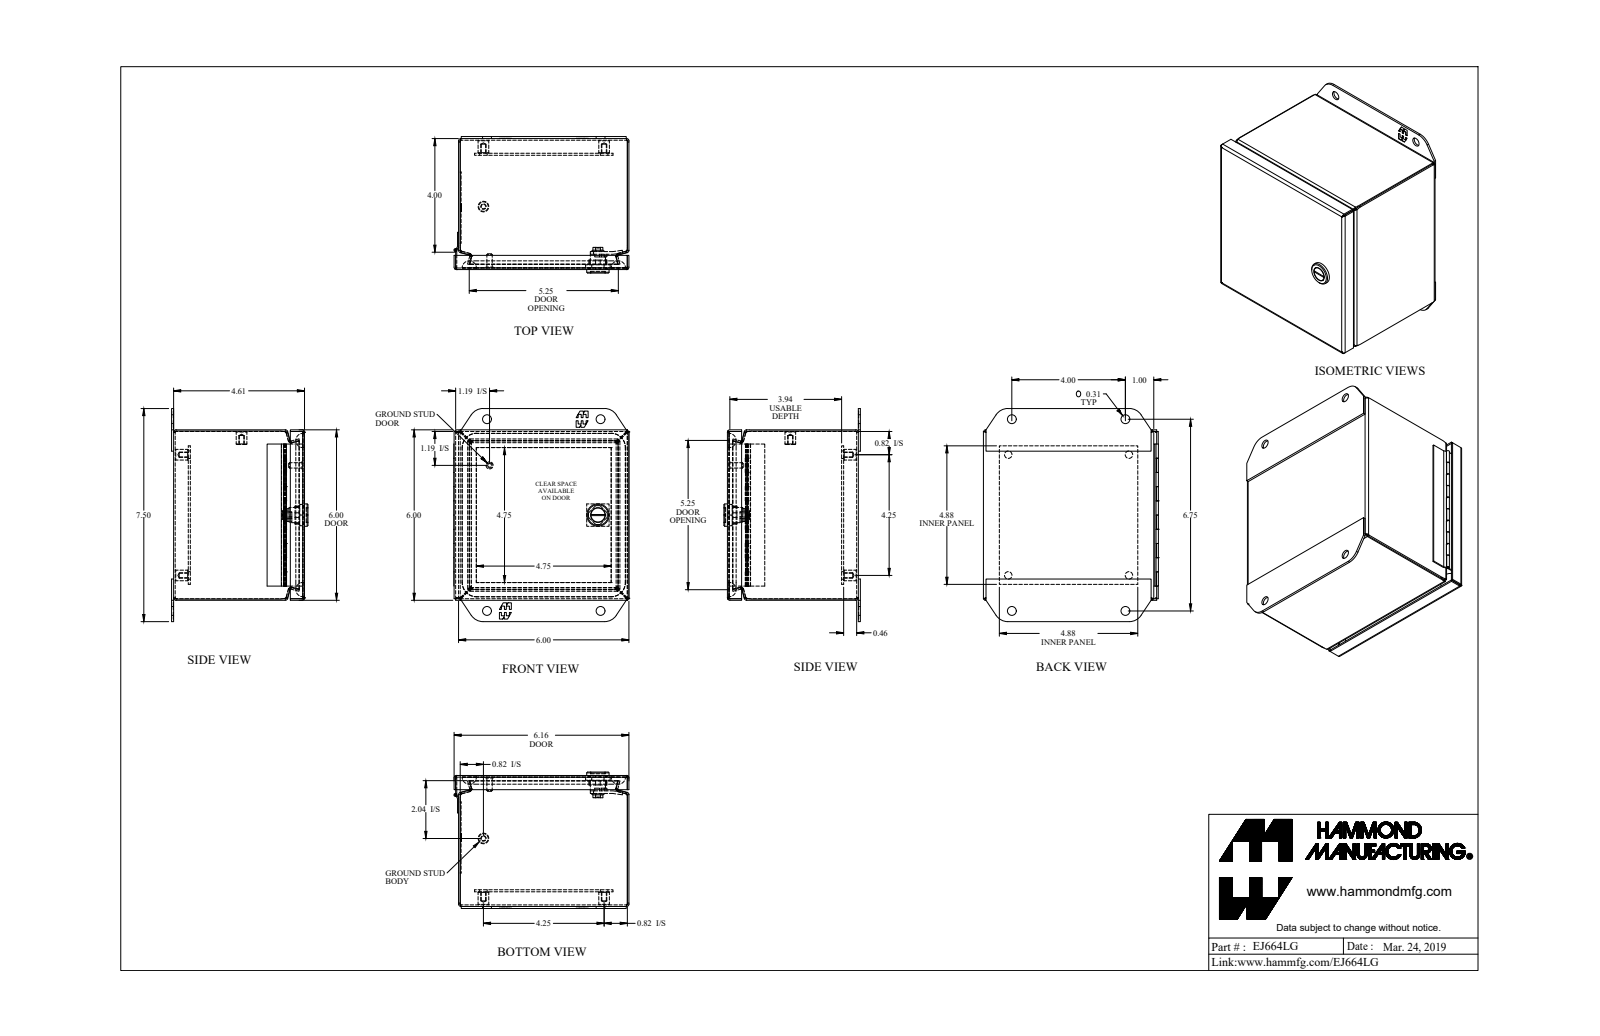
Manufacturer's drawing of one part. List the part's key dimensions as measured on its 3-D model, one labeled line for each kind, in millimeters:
Part name (STEP PRODUCT): EJ664LG_Default
STEP written by: SolidWorks 2019 (CONFIG_CONTROL_DESIGN)
Units: millimetres
Bodies: 16 solids, 611 faces (345 planar, 174 cylindrical, 92 other)
Overall size (bounding box): 190.5 × 156.6 × 122
Volume: 269 900 mm³ · Surface area: 349 000 mm²
Round holes (diameter × count): ⌀4 ×5, ⌀6.7 ×4, ⌀8 ×4, ⌀1.3 ×1, ⌀13.1 ×1
Round bosses / shafts (diameter × count): ⌀9.5 ×5, ⌀20 ×1, ⌀13.6 ×1, ⌀12.6 ×1, ⌀11 ×1, ⌀6.4 ×1, ⌀4.8 ×1, ⌀2.5 ×1
Partial cylindrical surfaces — rounded edges, fillets, slot ends (radius × count): R0.7 ×16, R2.2 ×16, R7.1 ×10, R6.4 ×4, R12.7 ×4, R12.7 ×4, R1.5 ×2, R13.7 ×2
Main face-to-face distances: 1.4, 151, 115.7, 152.4, 149.5, 1.8, 15, 117.1, 114.2, 11.7
Hole centre spacings: 31.9, 109.5, 139.7, 54.3, 85.8, 101.6, 108, 108
